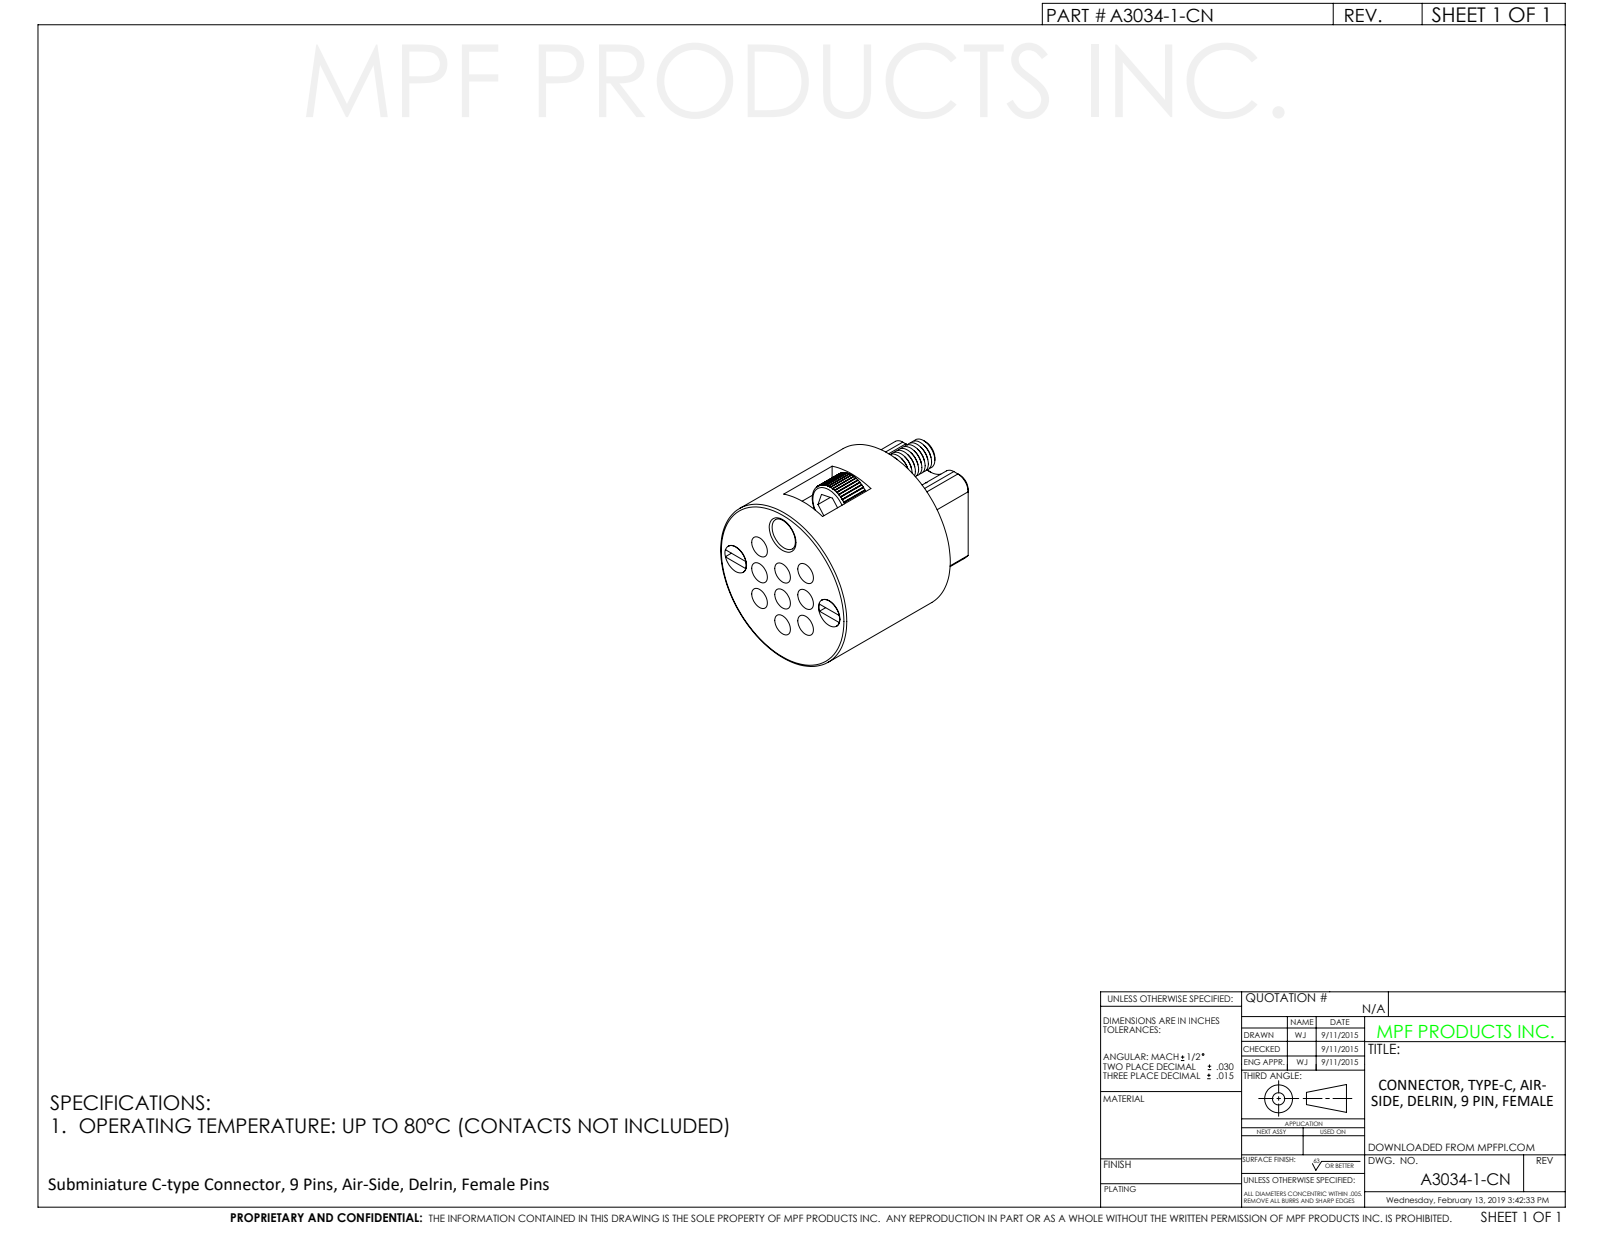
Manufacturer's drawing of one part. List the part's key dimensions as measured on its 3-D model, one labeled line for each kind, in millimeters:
Part name (STEP PRODUCT): A3034-1-CN
STEP written by: SolidWorks 2012 (CONFIG_CONTROL_DESIGN)
Units: millimetres
Bodies: 1 solid, 454 faces (246 planar, 130 cylindrical, 78 other)
Overall size (bounding box): 18.52 × 15.49 × 15.49
Volume: 2 416 mm³ · Surface area: 2 405 mm²
Round holes (diameter × count): ⌀1.17 ×9, ⌀1.93 ×9, ⌀2.95 ×1
Round bosses / shafts (diameter × count): ⌀2.62 ×2, ⌀15.49 ×1, ⌀4.32 ×1, ⌀2.79 ×1
Partial cylindrical surfaces — rounded edges, fillets, slot ends (radius × count): R1.27 ×5, R1.32 ×1, R2.4 ×1, R2.41 ×1, R5.84 ×1
Main face-to-face distances: 12.95, 4.44, 8.51, 5.46, 5.54, 9.98, 18.49, 11, 1.02, 7.49
Hole centre spacings: 3.15, 2.77, 5.02, 3.17, 5.68, 6.32, 3.91, 5.54
